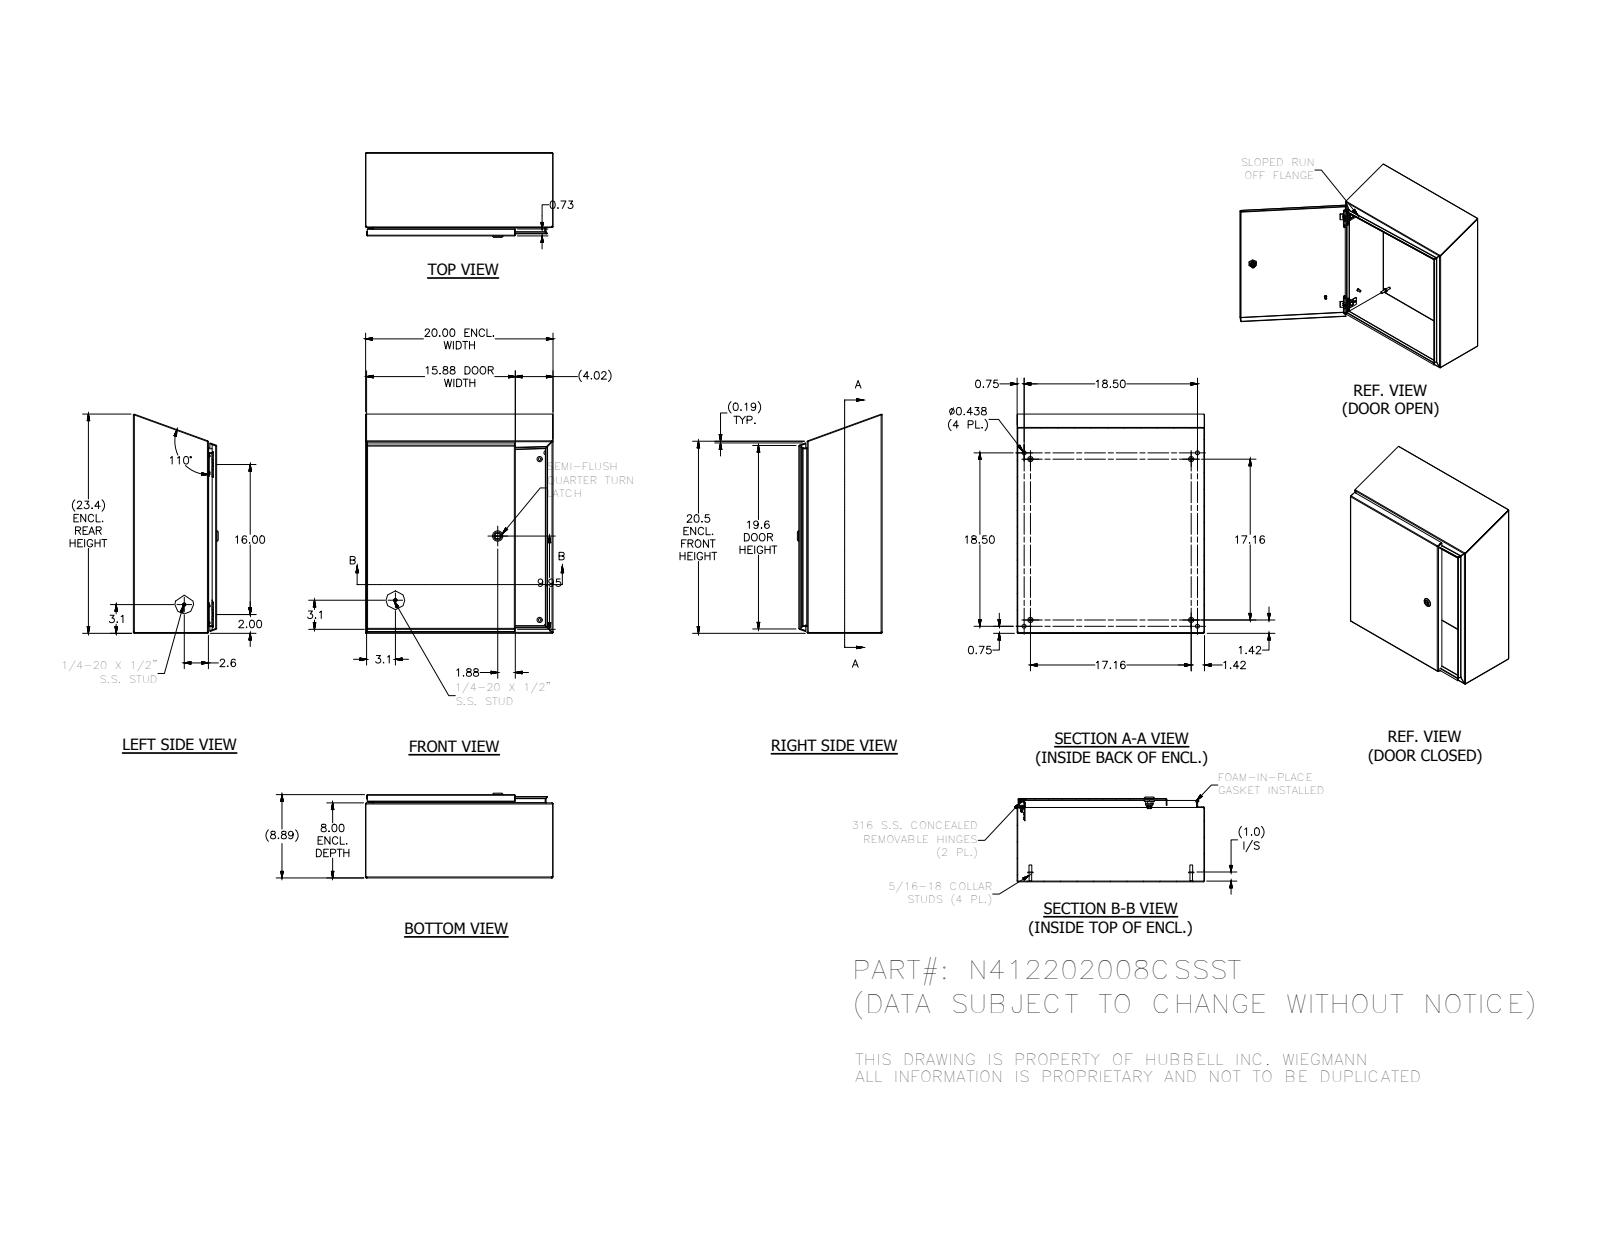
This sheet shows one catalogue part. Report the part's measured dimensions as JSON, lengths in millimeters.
{"part_name": "N412202008CSSST", "step_written_by": "SolidWorks 2018 (AUTOMOTIVE_DESIGN)", "units": "millimeters", "bodies": {"solids": 36, "faces": 1426, "planar": 538, "cylindrical": 509, "other": 379}, "overall_size": [594.1, 508, 229.7], "volume_mm3": 2083000, "surface_area_mm2": 2231000, "round_holes": [[2.4, 4], [3.9, 4], [4.2, 4], [4.4, 4], [4.7, 4], [11.1, 4], [4, 3], [4.7, 1], [5, 1], [8, 1], [10, 1], [10.2, 1]], "round_bosses_or_shafts": [[6.4, 10], [14.3, 4], [9.1, 4], [8.1, 4], [7.6, 4], [7, 4], [6.5, 4], [4.2, 4]], "partial_cylinders_radius": [[0.8, 29], [1.3, 26], [2.7, 19], [0.4, 18], [0.5, 16], [3.2, 16], [0.8, 8], [13.3, 6]], "face_to_face_distances": [1.9, 223.9, 222, 225.7, 506.1, 504.2, 508, 201.3, 22.5, 20.7], "hole_center_spacings": [406.4, 469.9, 12.7, 16.7, 16.8, 24.2, 33.2, 33.3]}
